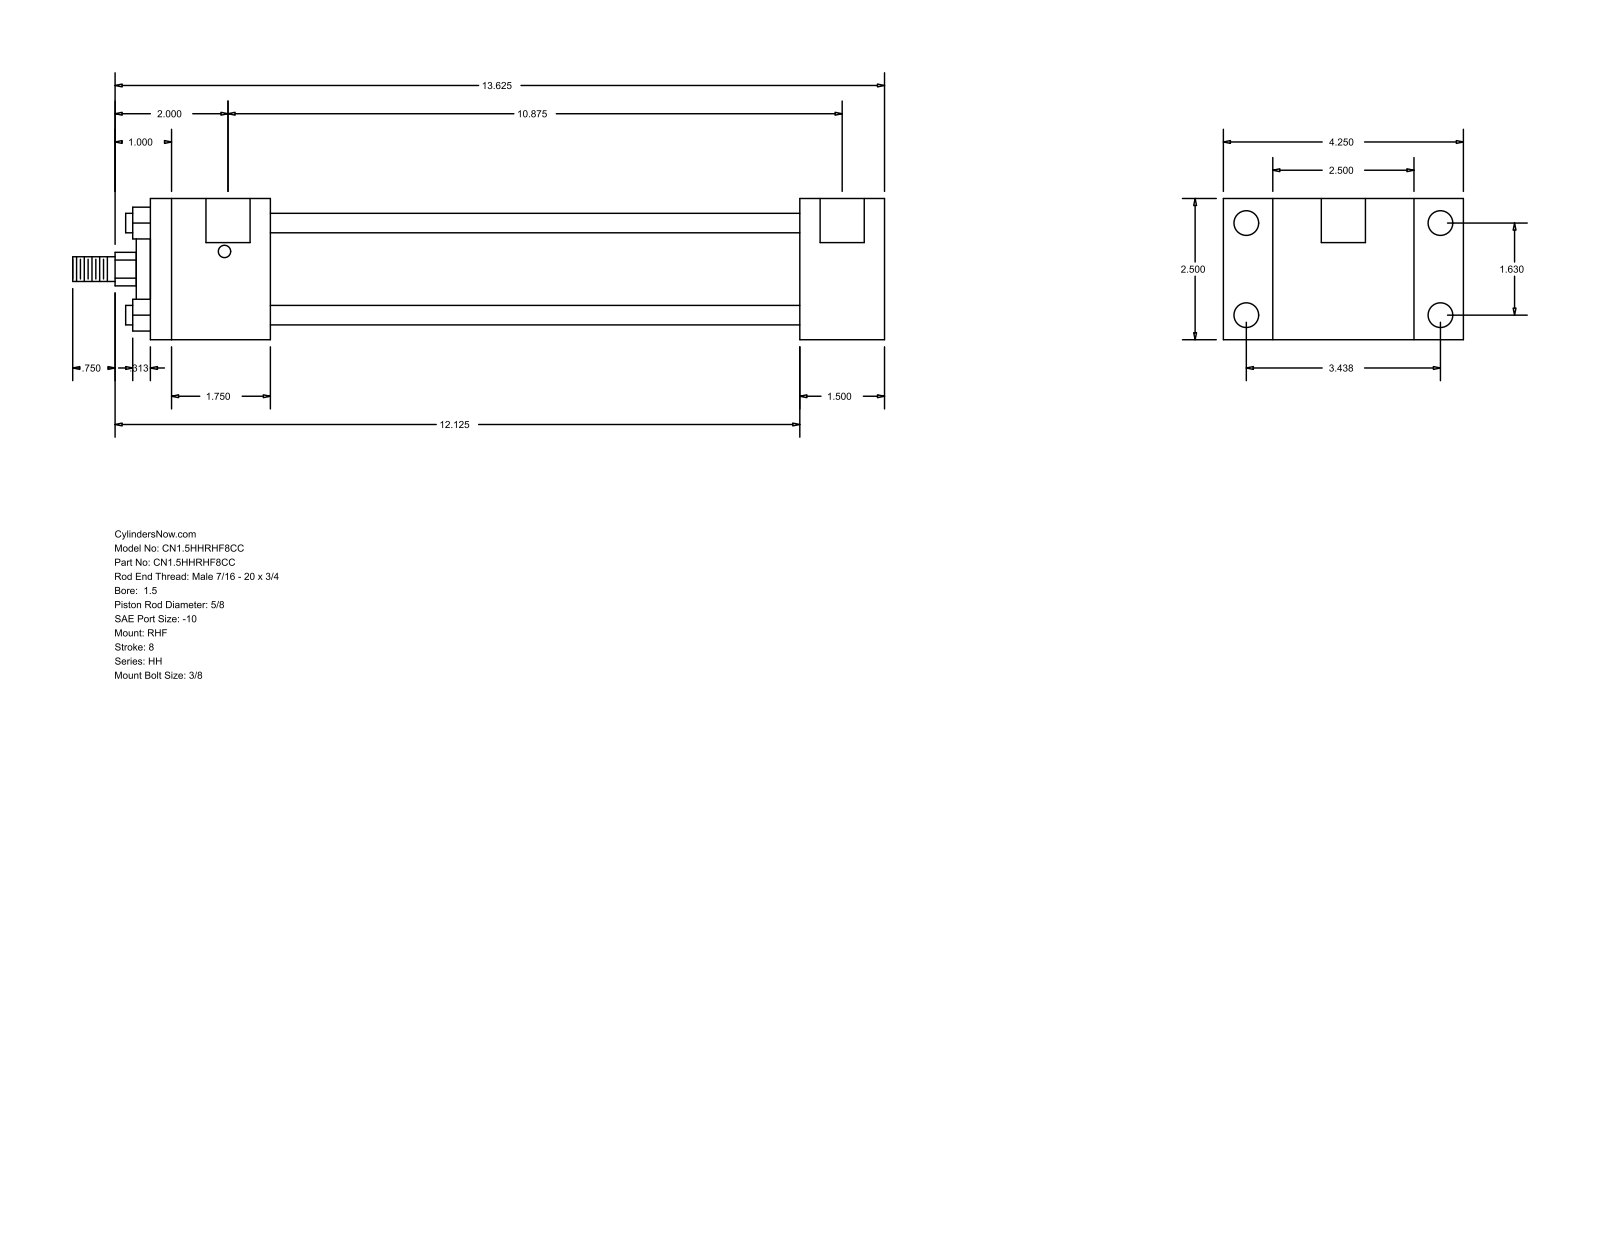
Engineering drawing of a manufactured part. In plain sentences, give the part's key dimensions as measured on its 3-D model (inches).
The part is named "HH_RHF__0150_0.625". Its 3-D file was written by "GSSL Pune (CONFIG_CONTROL_DESIGN)". It is 0 solids with 88 faces: 60 planar, 28 cylindrical and 0 other. Overall it measures 14.375 by 4.25 by 2.5 inches. Round holes: 4 of diameter 0.219, 4 of diameter 0.438, 2 of diameter 0.781. Round bosses or shafts: 4 of diameter 0.345, 1 of diameter 1.75, 1 of diameter 1.125, 1 of diameter 0.625, 1 of diameter 0.437. Partial cylindrical surfaces (rounded edges, fillets, slot ends): 1 of radius 0.297. The main face-to-face distances are 2.5, 0.875, 3.375, 1.5, 11.5, 13, 4.25, 2.125, 9.375, 10.875. The hole center spacings are 0.063, 1.63, 3.438, 3.805, 10.937, 11, 10.875.
